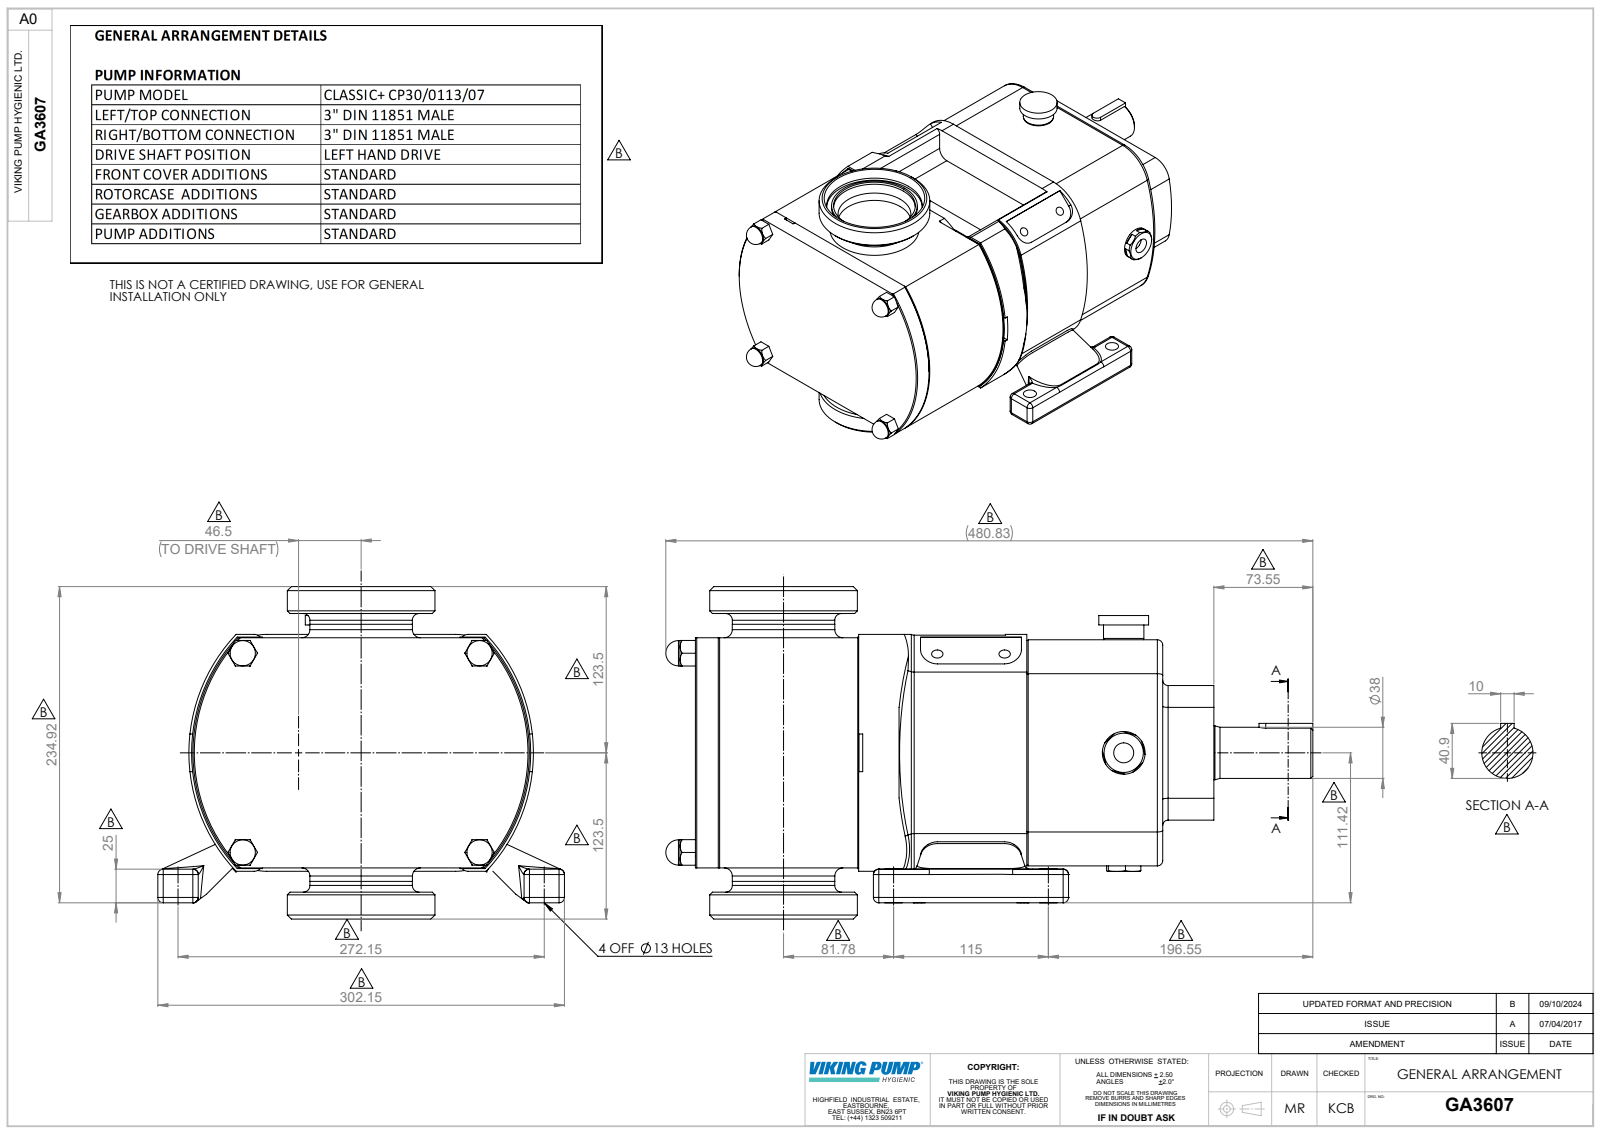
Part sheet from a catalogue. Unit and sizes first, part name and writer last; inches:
Units: inches
Overall size (bounding box): 18.93 × 11.896 × 9.724
Round holes (diameter × count): ⌀0.335 ×4, ⌀0.398 ×4, ⌀0.512 ×4, ⌀0.358 ×2, ⌀1.378 ×2, ⌀0.585 ×1, ⌀2.843 ×1, ⌀3.189 ×1, ⌀3.732 ×1
Round bosses / shafts (diameter × count): ⌀0.74 ×4, ⌀3.268 ×2, ⌀1.969 ×2, ⌀4.319 ×1, ⌀3.346 ×1, ⌀3 ×1, ⌀2.996 ×1, ⌀1.575 ×1
Partial cylindrical surfaces — rounded edges, fillets, slot ends (radius × count): R0.118 ×34, R0.157 ×24, R0.394 ×12, R0.495 ×8, R0.236 ×6, R0.492 ×4, R0.787 ×4, R1.398 ×4
Main face-to-face distances: 0.059, 6.673, 5.472, 1.496, 6.702, 6.732, 8.467, 15.169, 1.142, 1.201
Hole centre spacings: 2.506, 1.97, 3.399, 3.543, 4.528, 7.148, 7.598, 8.69
Volume: 795.1 in³ · Surface area: 898.6 in²
Bodies: 3 solids, 718 faces (270 planar, 248 cylindrical, 200 other)
Part name (STEP PRODUCT): GA3607; Copy of CP30-0113-07 V L^GA3607; Copy of Z94-5031-55 - 3 INCH DIN11851^GA3607
STEP written by: SolidWorks 2023 (AUTOMOTIVE_DESIGN)
